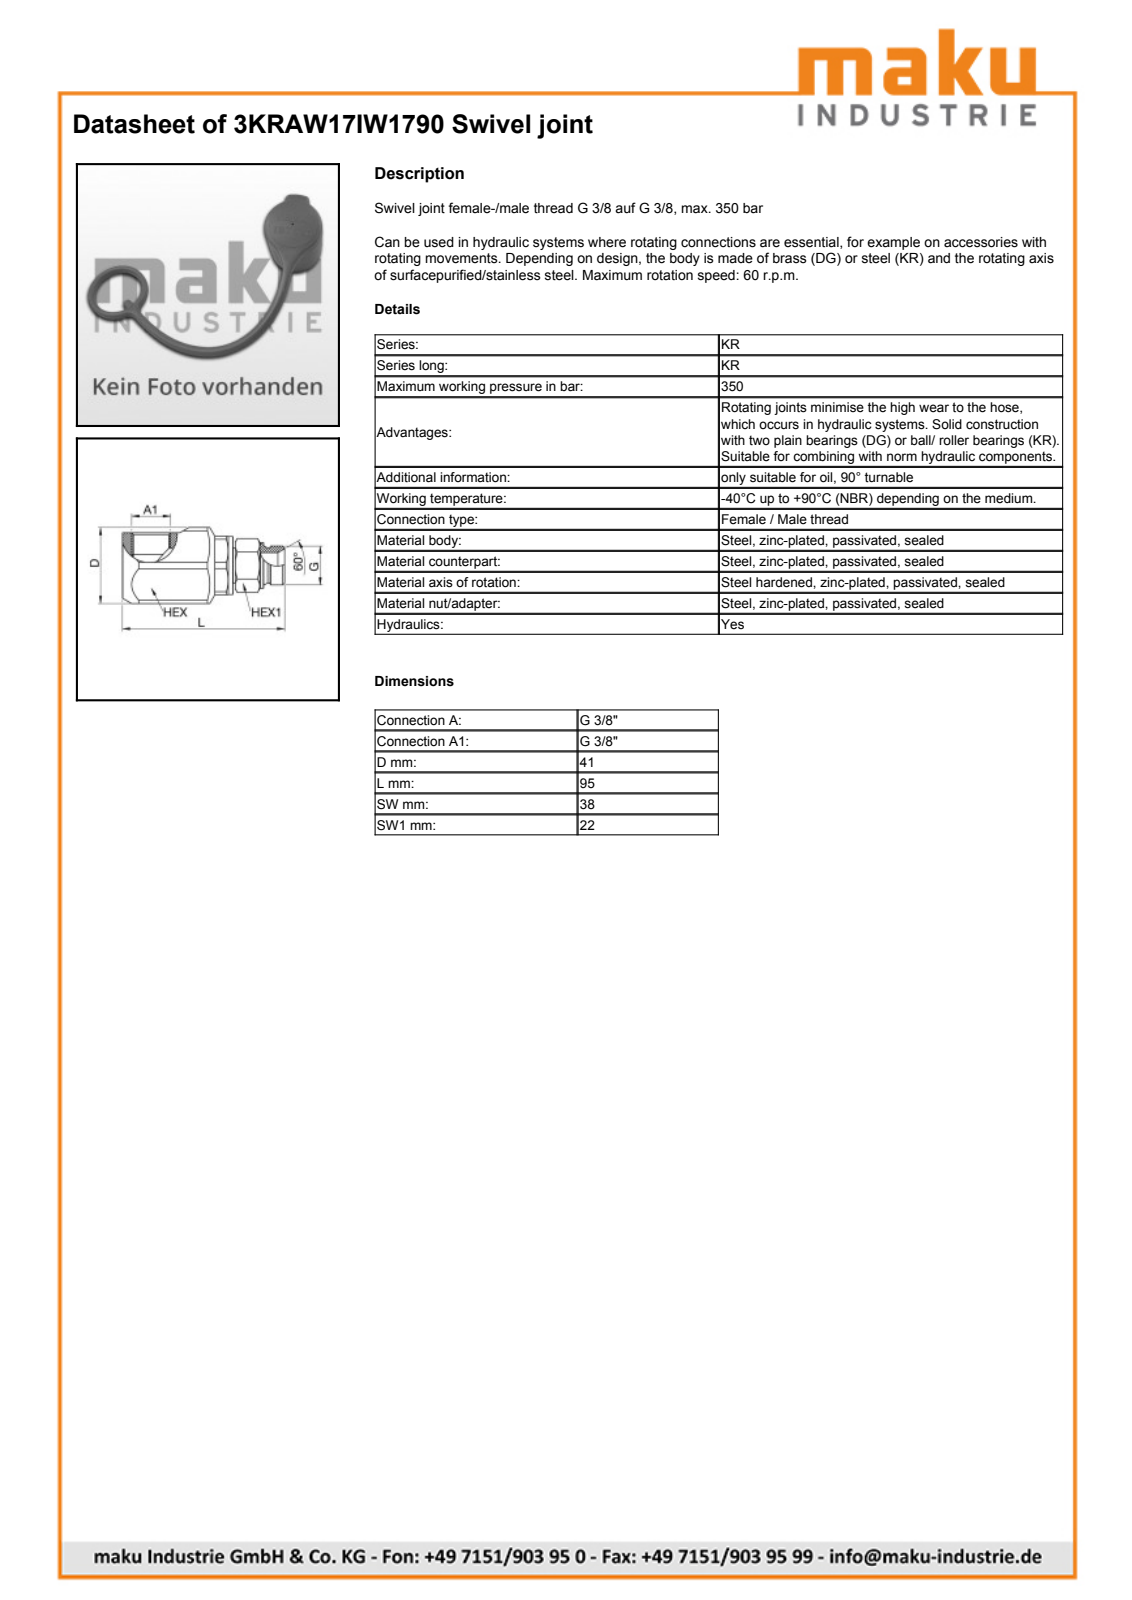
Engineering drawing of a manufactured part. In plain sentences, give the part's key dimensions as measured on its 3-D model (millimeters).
The part is named "3kraw17iw1790". Its 3-D file was written by "SolidWorks 2009 (AUTOMOTIVE_DESIGN)". It is 1 solid with 101 faces: 28 planar, 34 cylindrical and 39 other. Overall it measures 94.9 by 41 by 38 millimeters. Its volume is 78 054 cubic millimeters and its surface area 13 026 square millimeters. Round holes: 1 of diameter 9, 1 of diameter 14.95, 1 of diameter 15.3, 1 of diameter 21. Round bosses or shafts: 1 of diameter 29.7, 1 of diameter 28.04, 1 of diameter 16.66, 1 of diameter 14.9, 1 of diameter 14.4. Partial cylindrical surfaces (rounded edges, fillets, slot ends): 1 of radius 9.61, 1 of radius 16.25, 1 of radius 20.5. The main face-to-face distances are 38, 4, 30, 34, 26, 8, 2, 36, 22, 66.9.
